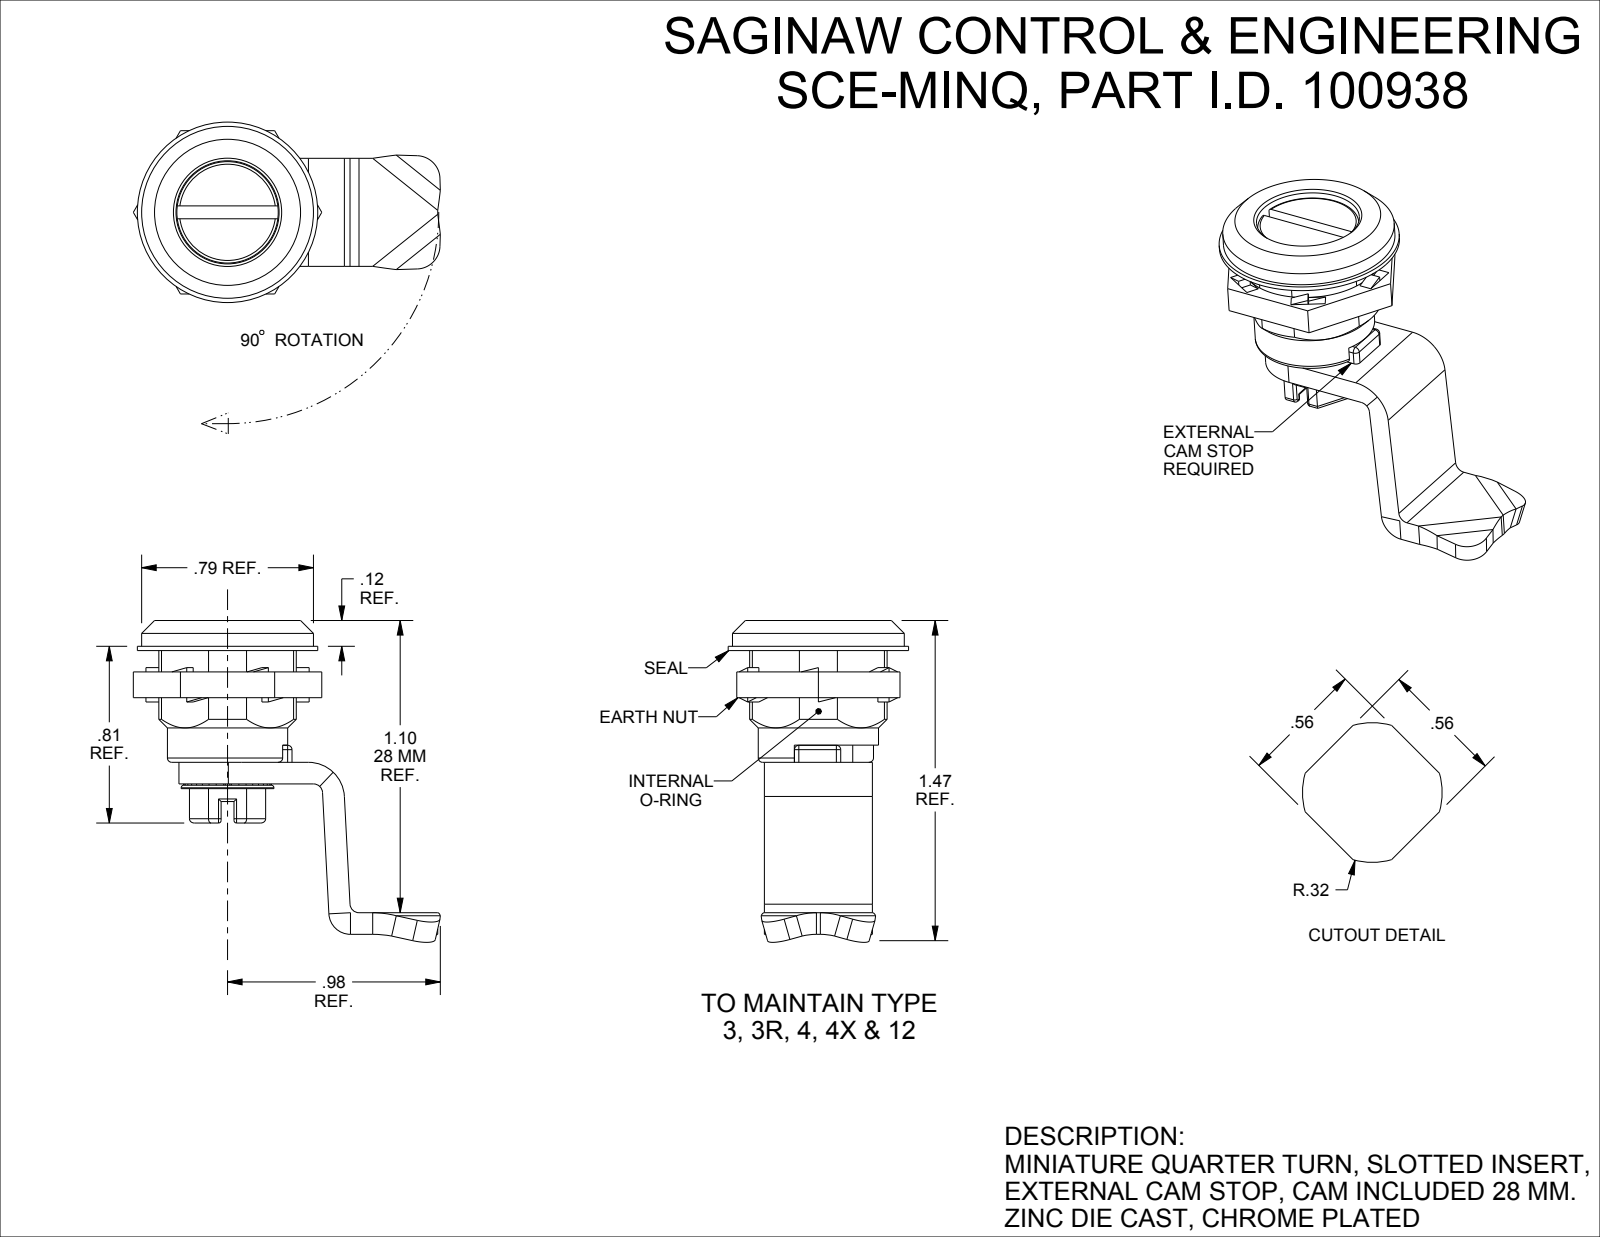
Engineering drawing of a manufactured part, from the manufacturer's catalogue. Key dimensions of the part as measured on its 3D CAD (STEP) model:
Part name (STEP PRODUCT): SCE-MINQ
STEP written by: SolidWorks 2021 (AUTOMOTIVE_DESIGN)
Units: inches
Bodies: 8 solids, 369 faces (133 planar, 96 cylindrical, 140 other)
Overall size (bounding box): 1.39 × 1.334 × 1.316
Volume: 0.301 in³ · Surface area: 9.478 in²
Round holes (diameter × count): ⌀0.161 ×1, ⌀0.315 ×1, ⌀0.327 ×1, ⌀0.48 ×1, ⌀0.581 ×1
Round bosses / shafts (diameter × count): ⌀0.827 ×1, ⌀0.787 ×1, ⌀0.551 ×1, ⌀0.469 ×1, ⌀0.453 ×1, ⌀0.374 ×1, ⌀0.311 ×1, ⌀0.197 ×1
Partial cylindrical surfaces — rounded edges, fillets, slot ends (radius × count): R0.031 ×4, R0.15 ×4, R0.02 ×3, R0.039 ×3, R0.181 ×1, R0.193 ×1, R0.236 ×1, R0.315 ×1
Main face-to-face distances: 0.118, 0.65, 0.472, 0.531, 0.02, 0.177, 0.157, 0.512, 0.571, 1.043
